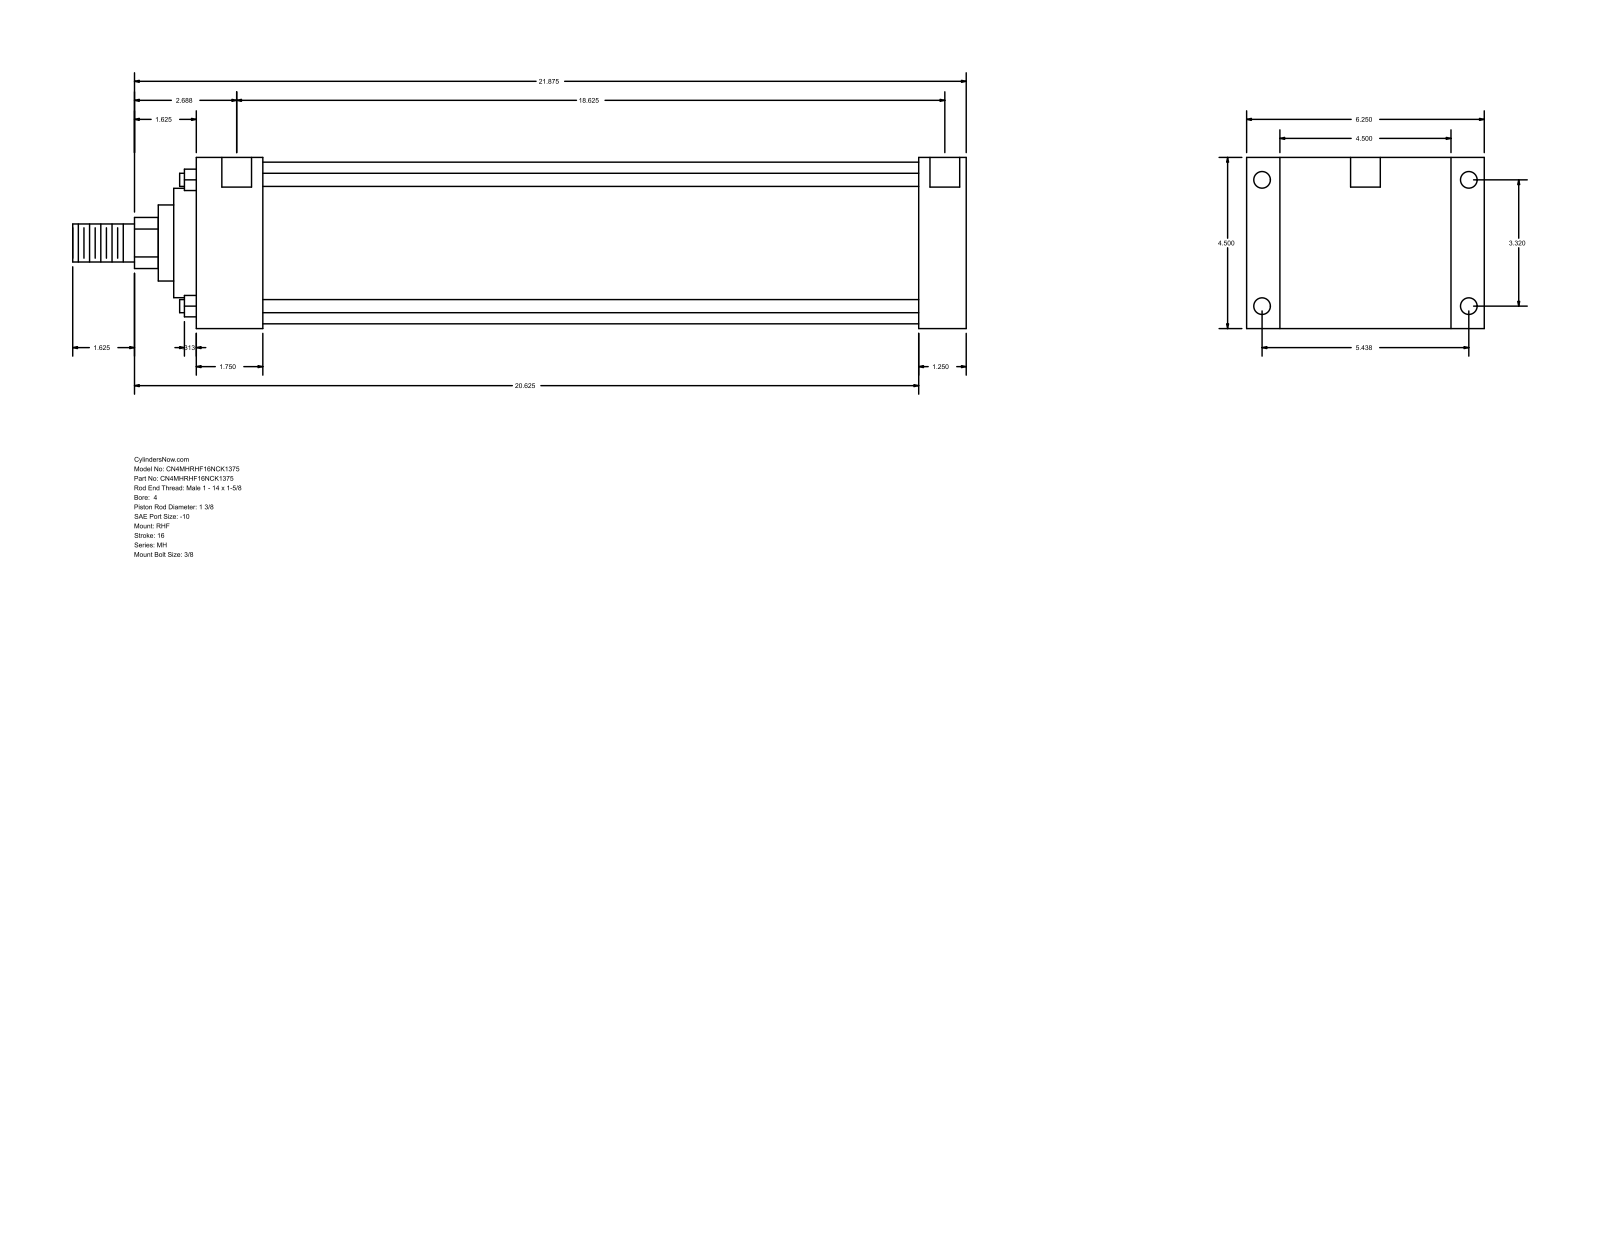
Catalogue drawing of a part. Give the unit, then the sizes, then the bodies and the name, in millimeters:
Units: millimetres
Overall size (bounding box): 596.9 × 158.75 × 114.3
Round holes (diameter × count): ⌀8.73 ×4, ⌀11.13 ×4, ⌀19.84 ×2
Round bosses / shafts (diameter × count): ⌀8.76 ×4, ⌀107.95 ×1, ⌀73.03 ×1, ⌀50.8 ×1, ⌀34.92 ×1, ⌀25.4 ×1
Partial cylindrical surfaces — rounded edges, fillets, slot ends (radius × count): R17.06 ×1
Main face-to-face distances: 114.3, 31.74, 482.61, 514.35, 22.23, 136.53, 44.45, 438.16, 469.9, 158.76
Hole centre spacings: 84.32, 138.12, 161.82, 476.25, 1.58, 1.59, 473.08, 474.66
Bodies: 0 solids, 90 faces (61 planar, 29 cylindrical, 0 other)
Part name (STEP PRODUCT): MH_RHF__0400_1.375
STEP written by: GSSL Pune (CONFIG_CONTROL_DESIGN)
